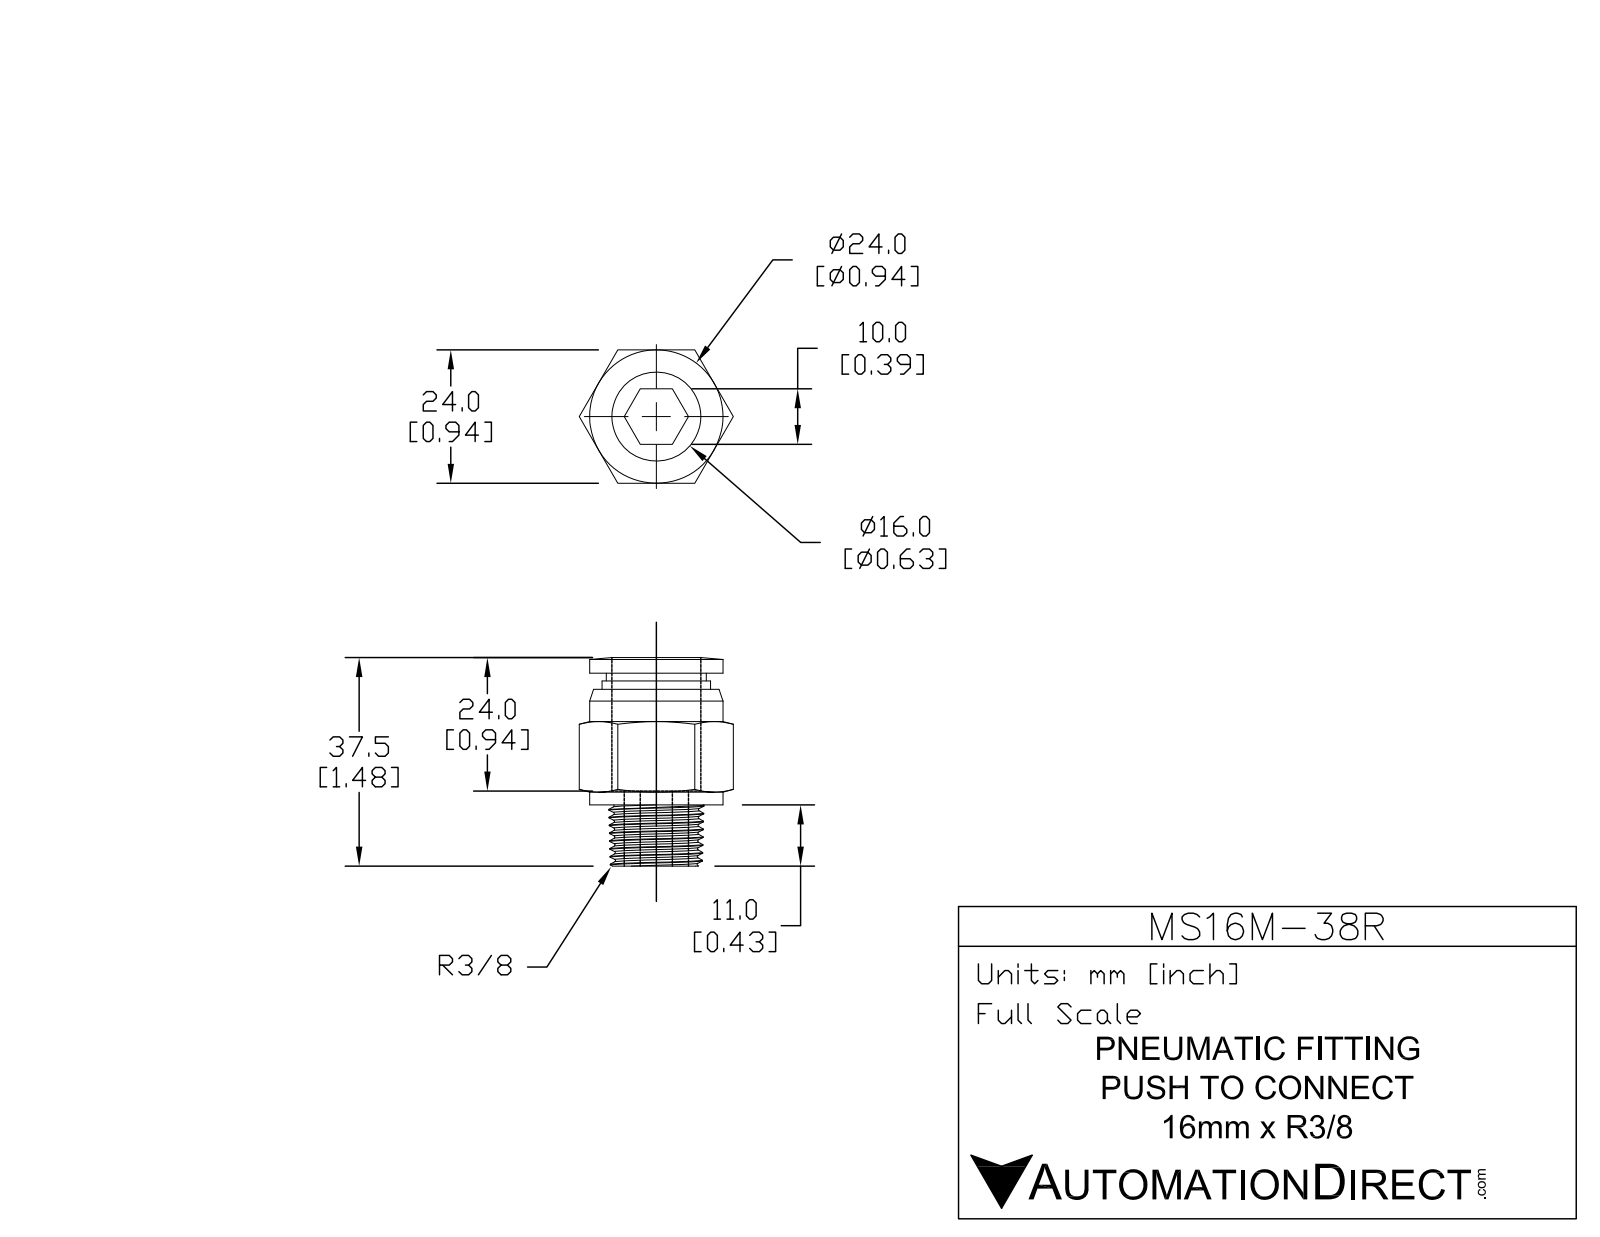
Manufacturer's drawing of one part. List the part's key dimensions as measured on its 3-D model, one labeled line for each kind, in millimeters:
Part name (STEP PRODUCT): MS16M-38R
STEP written by: SolidWorks 2015 (AUTOMOTIVE_DESIGN)
Units: millimetres
Bodies: 1 solid, 53 faces (13 planar, 14 cylindrical, 26 other)
Overall size (bounding box): 37.5 × 27.7 × 25.2
Volume: 8 230 mm³ · Surface area: 5 401 mm²
Round holes (diameter × count): ⌀10 ×1, ⌀16.3 ×1
Round bosses / shafts (diameter × count): ⌀25.2 ×1, ⌀24 ×1, ⌀22 ×1, ⌀20.2 ×1, ⌀18 ×1
Main face-to-face distances: 24, 21.2, 2.5, 23.7, 21.7, 19.2, 2, 11, 13.5, 32.7
